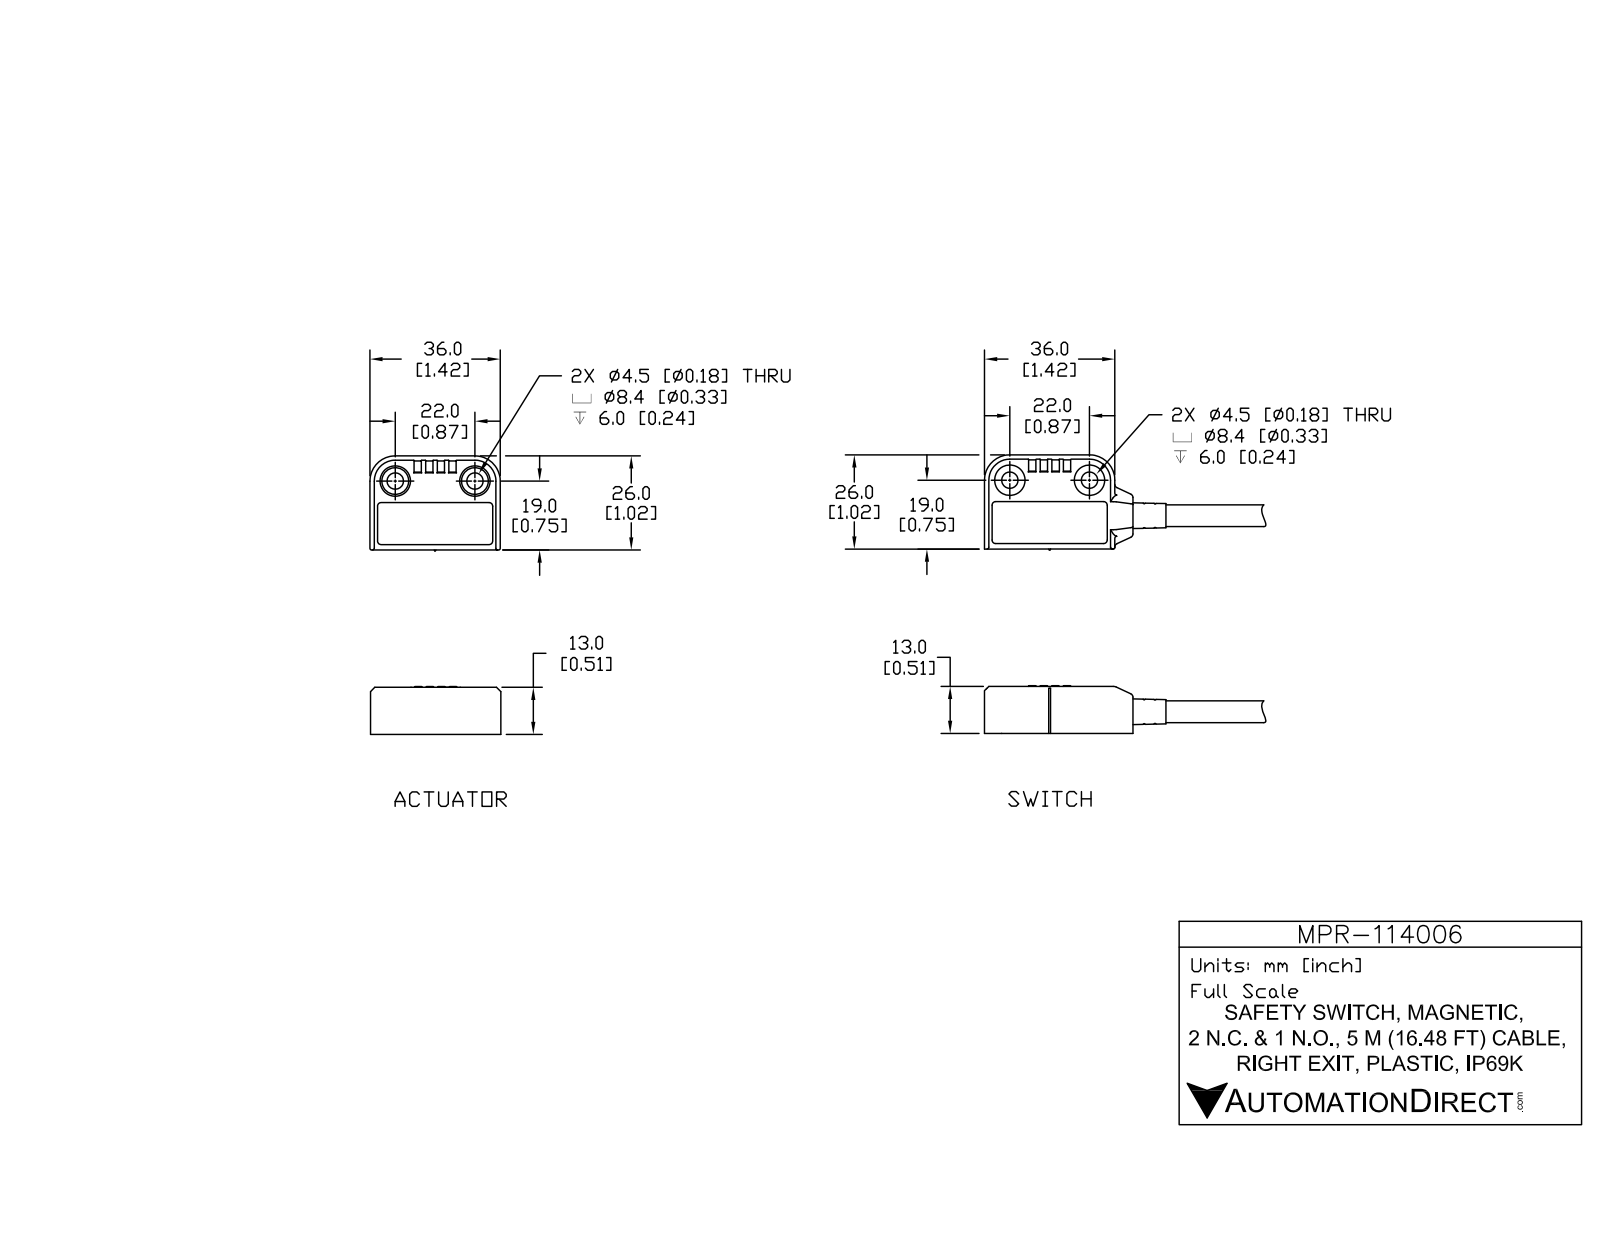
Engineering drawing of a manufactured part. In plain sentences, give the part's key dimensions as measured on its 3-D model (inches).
The part is named "MPR-114006_1; MPR-114006_2; MPR-114006". Its 3-D file was written by "SolidWorks 2017 (AUTOMOTIVE_DESIGN)". It is 9 solids with 1110 faces: 486 planar, 325 cylindrical and 299 other. Overall it measures 7.658 by 2.087 by 0.528 inches. Its volume is 1.059 cubic inches and its surface area 29.57 square inches. Round holes: 4 of diameter 0.177, 4 of diameter 0.331, 2 of diameter 0.195, 1 of diameter 0.197, 1 of diameter 0.232, 1 of diameter 0.276. Round bosses or shafts: 3 of diameter 0.079, 2 of diameter 0.197, 2 of diameter 0.091, 1 of diameter 0.339, 1 of diameter 0.299, 1 of diameter 0.28, 1 of diameter 0.236. Partial cylindrical surfaces (rounded edges, fillets, slot ends): 85 of radius 0.02, 30 of radius 0.008, 28 of radius 0.012, 17 of radius 0.004, 13 of radius 0.039, 4 of radius 0.169, 4 of radius 0.201, 4 of radius 0.276. The main face-to-face distances are 0.055, 0.461, 0.39, 0.453, 0.047, 1.063, 0.059, 0.094, 0.445, 0.031. The hole center spacings are 0.866, 0.445, 0.974, 1.091, 1.393, 1.535, 1.763, 0.396.
